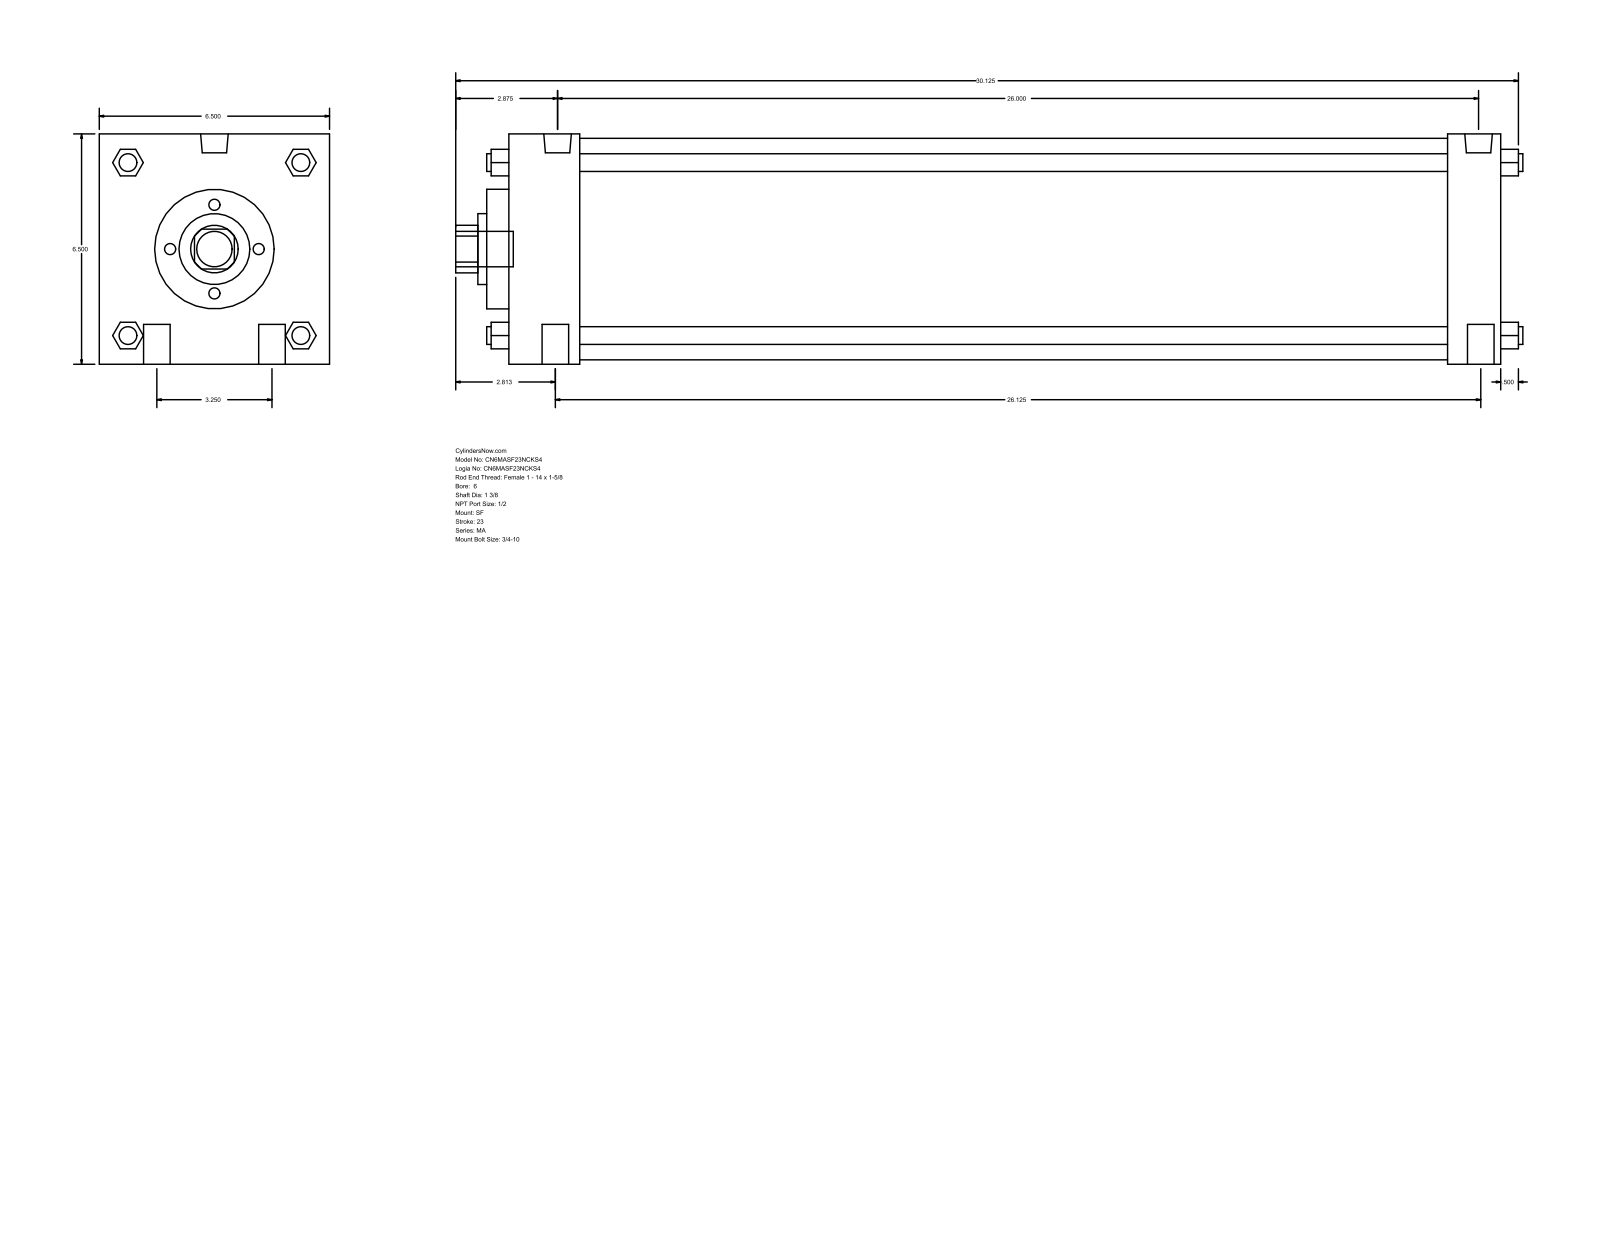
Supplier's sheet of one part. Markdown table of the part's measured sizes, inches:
| quantity | value |
| --- | --- |
| part name | MA_SF__0600_1.375 |
| STEP written by | GSSL Pune (CONFIG_CONTROL_DESIGN) |
| units | inches |
| bodies | 0 solids, 126 faces (95 planar, 31 cylindrical, 0 other) |
| overall size | 30.125 × 6.5 × 6.5 |
| round holes (diameter × count) | 1.375 × 1, 2 × 1, 3.375 × 1, 6.25 × 1 |
| round bosses / shafts (diameter × count) | 0.75 × 4, 0.5 × 4, 0.778 × 2, 0.687 × 2, 1 × 1 |
| partial cylindrical surfaces (radius × count) | 0.672 × 1 |
| main face-to-face distances | 6.5, 28, 26.5, 2, 1.5, 24.5, 26, 0.625, 28.625, 2.625 |
